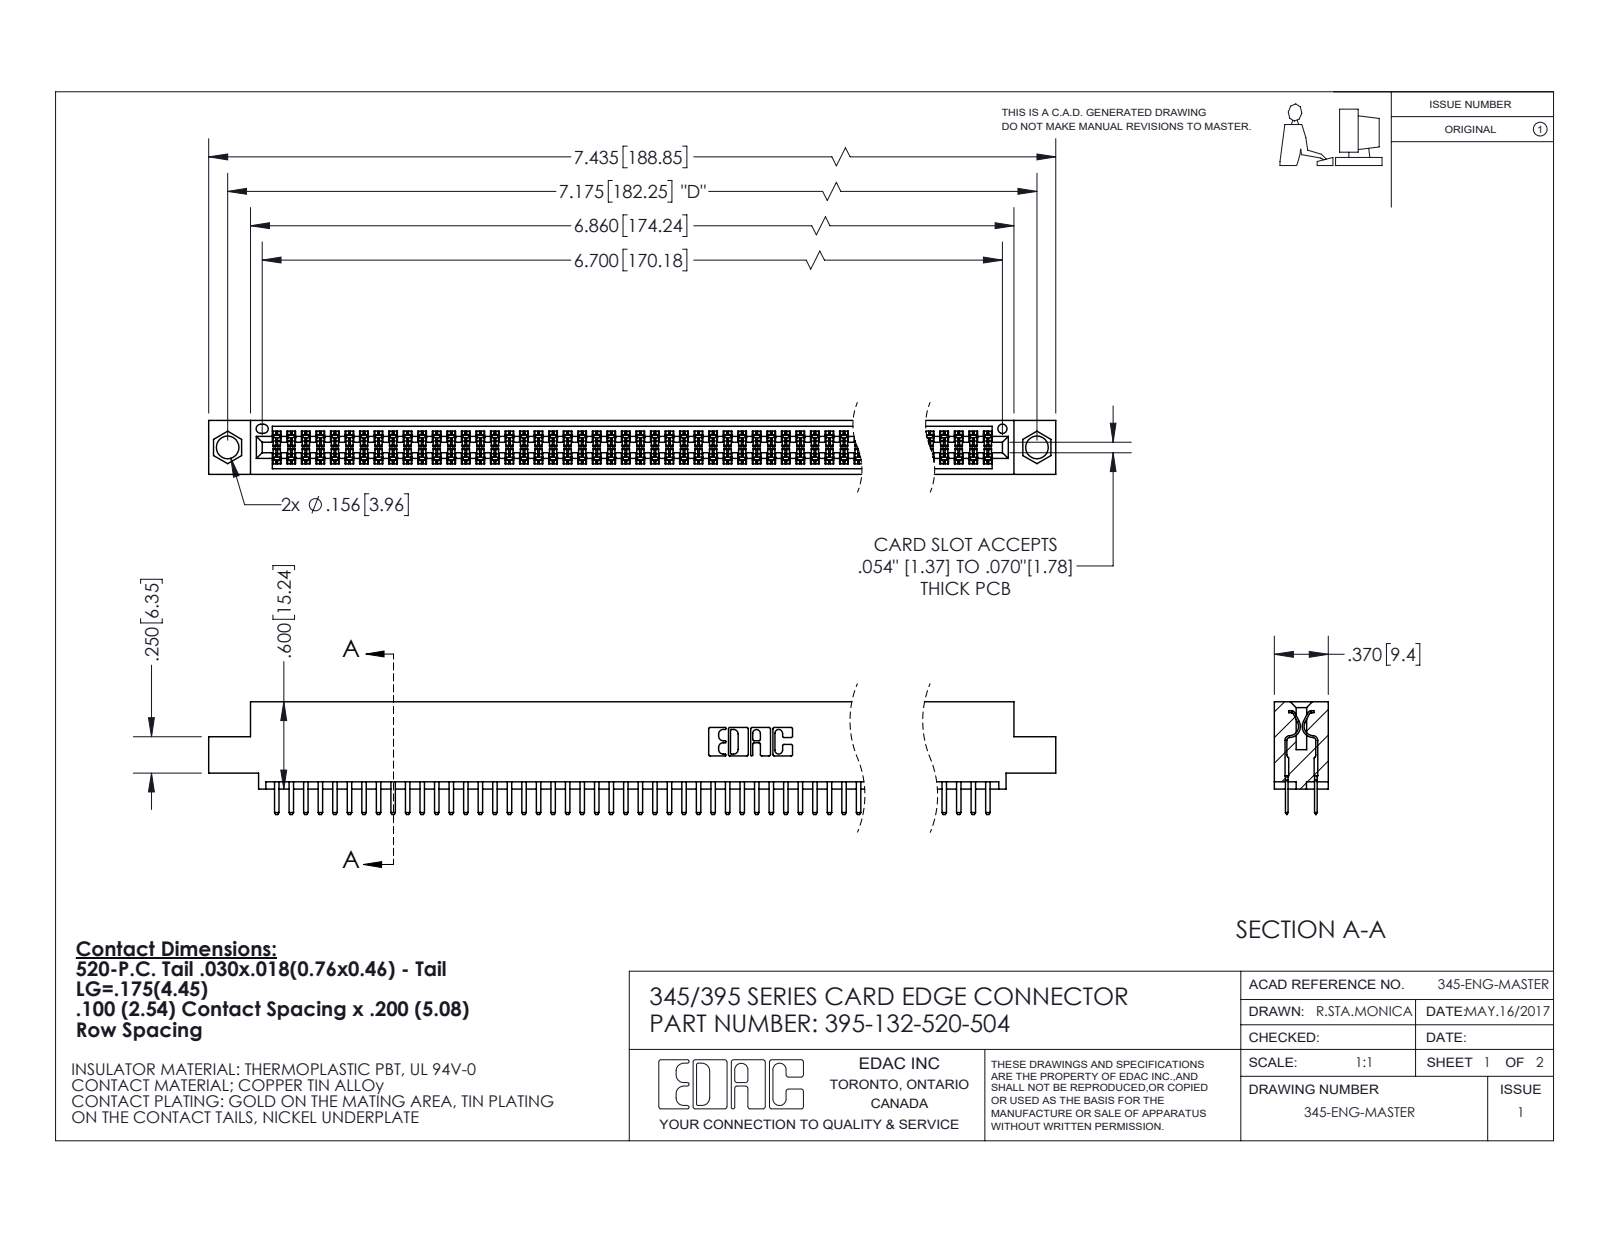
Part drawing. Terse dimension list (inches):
name: 345 Part_0.110 Offset - 0.156 Dia-TI; 345-292-001_345-293-120; 395-132-520-504
written by: SolidWorks 2020 (CONFIG_CONTROL_DESIGN)
unit: in
bodies: 133 solids, 7272 faces (4718 planar, 2554 cylindrical, 0 other)
size: 7.435 × 0.775 × 0.37
volume: 1.119 in³; area: 42.44 in²
holes: 2× ⌀0.156, 1× ⌀0.064
rounds: 198× R0.006, 136× R0.01, 22× R0.01, 6× R0.007, 6× R0.031, 3× R0.026, 2× R0.014, 2× R0.019
face distances: 0.072, 0.298, 0.2, 0.37, 0.098, 0.272, 0.025, 0.225, 0.022, 0.072
hole spacings: 0.27, 6.939, 7.175
